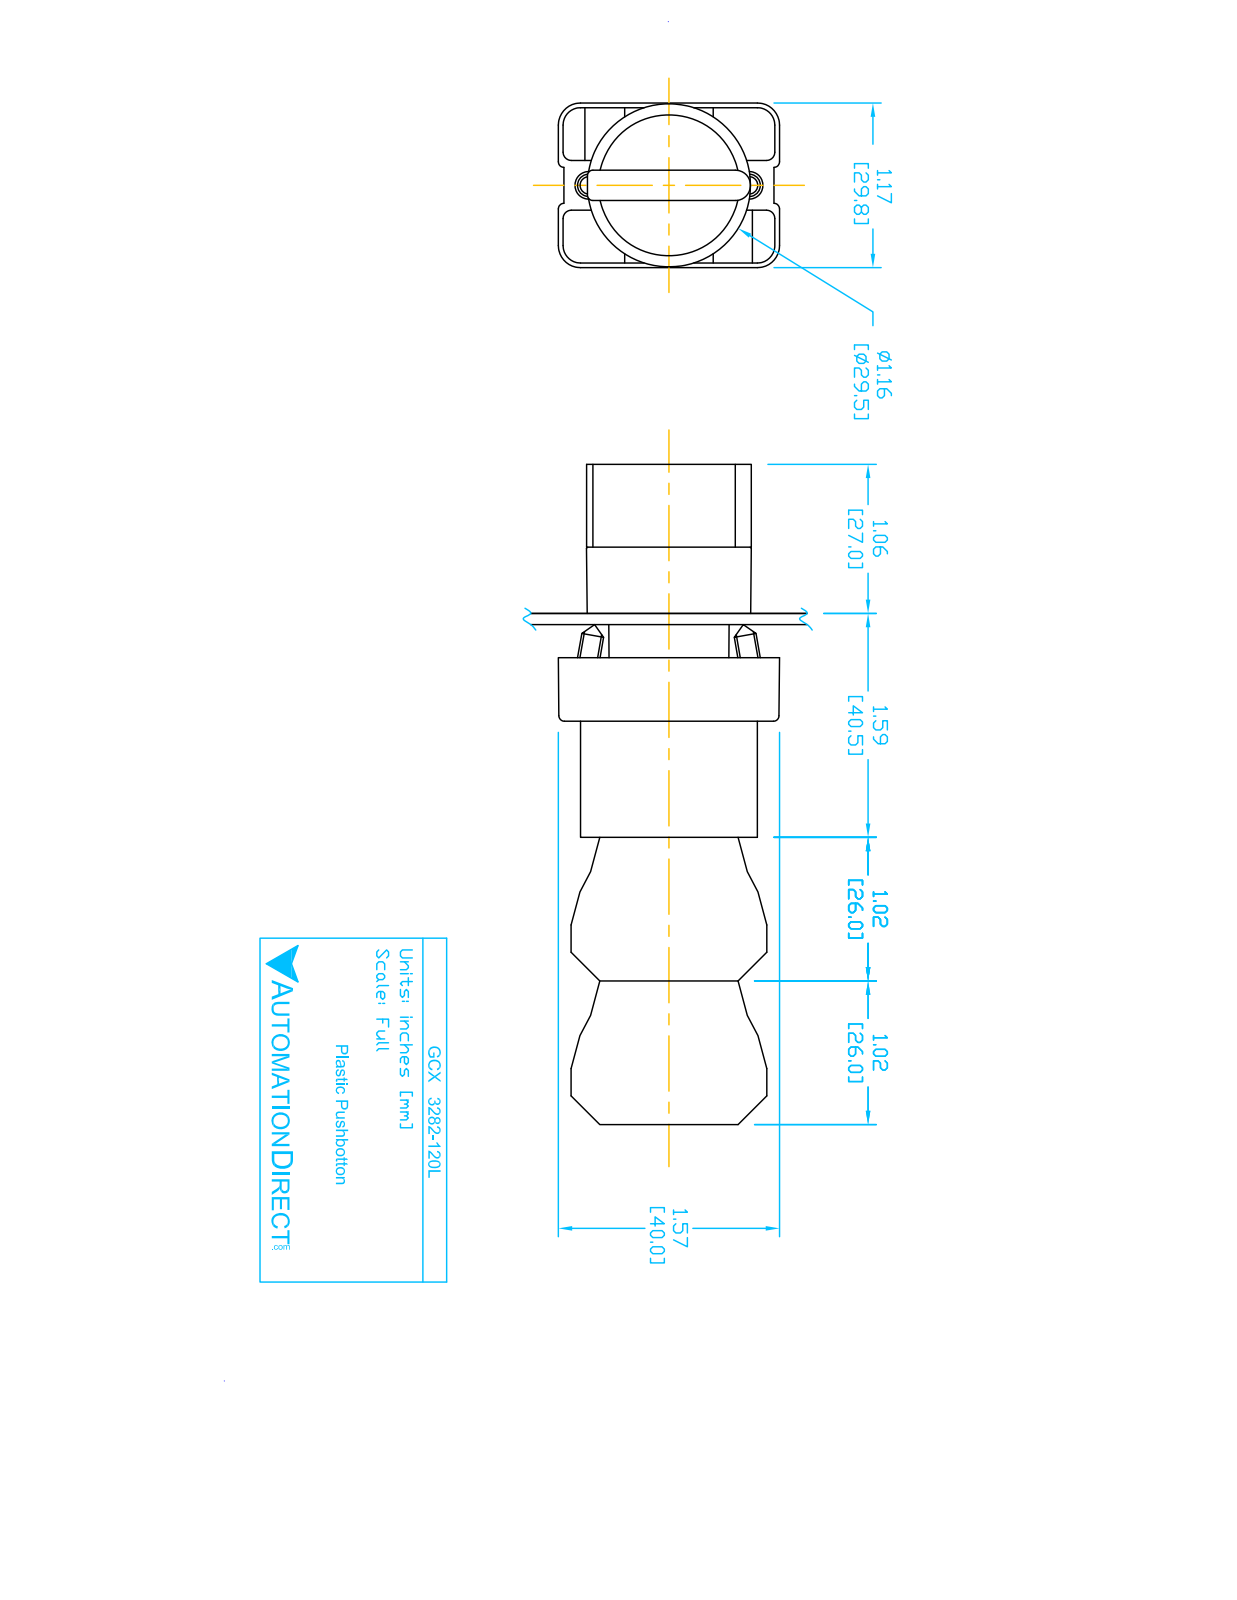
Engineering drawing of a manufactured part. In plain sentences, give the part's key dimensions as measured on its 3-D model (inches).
The part is named "ecx1030; ecx1040; ECX3029-2; ECX1050 (+2 more)". Its 3-D file was written by "SolidWorks 2016 (AUTOMOTIVE_DESIGN)". It is 11 solids with 724 faces: 488 planar, 193 cylindrical and 43 other. Overall it measures 4.677 by 1.581 by 1.177 inches. Its volume is 4.751 cubic inches and its surface area 59.22 square inches. Round holes: 4 of diameter 0.079, 2 of diameter 0.087, 2 of diameter 0.124, 2 of diameter 0.13, 1 of diameter 0.197, 1 of diameter 0.469, 1 of diameter 0.878, 1 of diameter 0.888, 1 of diameter 1.024. Round bosses or shafts: 4 of diameter 0.157, 1 of diameter 1.175, 1 of diameter 1.004, 1 of diameter 0.945, 1 of diameter 0.856, 1 of diameter 0.78, 1 of diameter 0.504. Partial cylindrical surfaces (rounded edges, fillets, slot ends): 24 of radius 0.059, 12 of radius 0.041, 12 of radius 0.124, 12 of radius 0.157, 9 of radius 0.039, 2 of radius 0.02, 2 of radius 0.063, 2 of radius 0.079. The main face-to-face distances are 0.579, 0.593, 1.024, 1.171, 0.014, 0.827, 1.85, 3.043, 2.02, 1.193. The hole center spacings are 0.236, 1.003, 0.974, 0.472, 0.539, 0.544, 1.083, 0.484.
